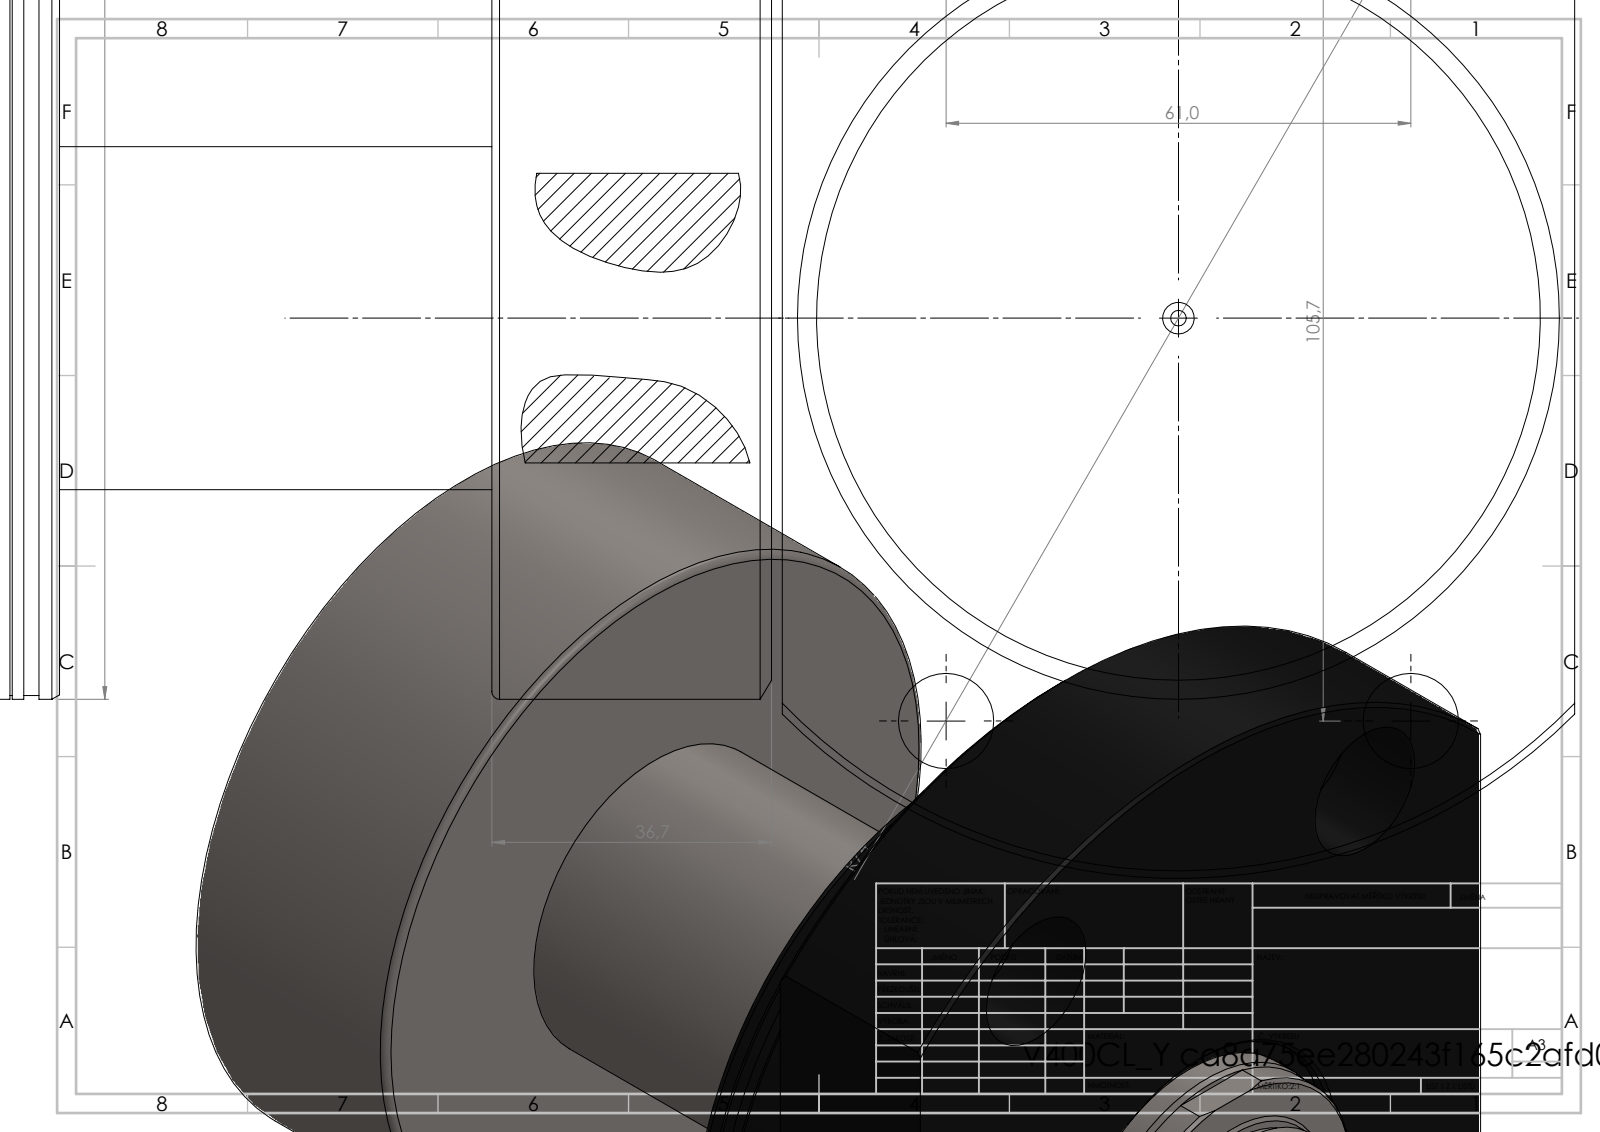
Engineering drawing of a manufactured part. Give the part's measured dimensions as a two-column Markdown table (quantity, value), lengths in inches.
| quantity | value |
| --- | --- |
| part name | V450CM_MALE_METRIC; V400CL_PC_Y; V400CL_VC_X |
| STEP written by | SolidWorks 2019 (CONFIG_CONTROL_DESIGN) |
| units | inches |
| bodies | 3 solids, 117 faces (30 planar, 51 cylindrical, 36 other) |
| overall size | 7.638 × 5.787 × 4.094 |
| volume | 55.79 in³ |
| surface area | 157.6 in² |
| round holes (diameter × count) | 0.492 × 4, 0.728 × 4, 0.081 × 1, 0.197 × 1, 0.236 × 1, 1.772 × 1, 1.949 × 1 |
| round bosses / shafts (diameter × count) | 3.937 × 1, 3.898 × 1, 1.299 × 1, 1.22 × 1 |
| partial cylindrical surfaces (radius × count) | 0.876 × 1, 2.894 × 1 |
| main face-to-face distances | 5.431, 1.445, 3.986, 3.679, 2.234, 1.752, 4.407, 2.963, 0.728, 1.024 |
| hole center spacings | 2.402, 2.402, 4.161, 4.805 |
